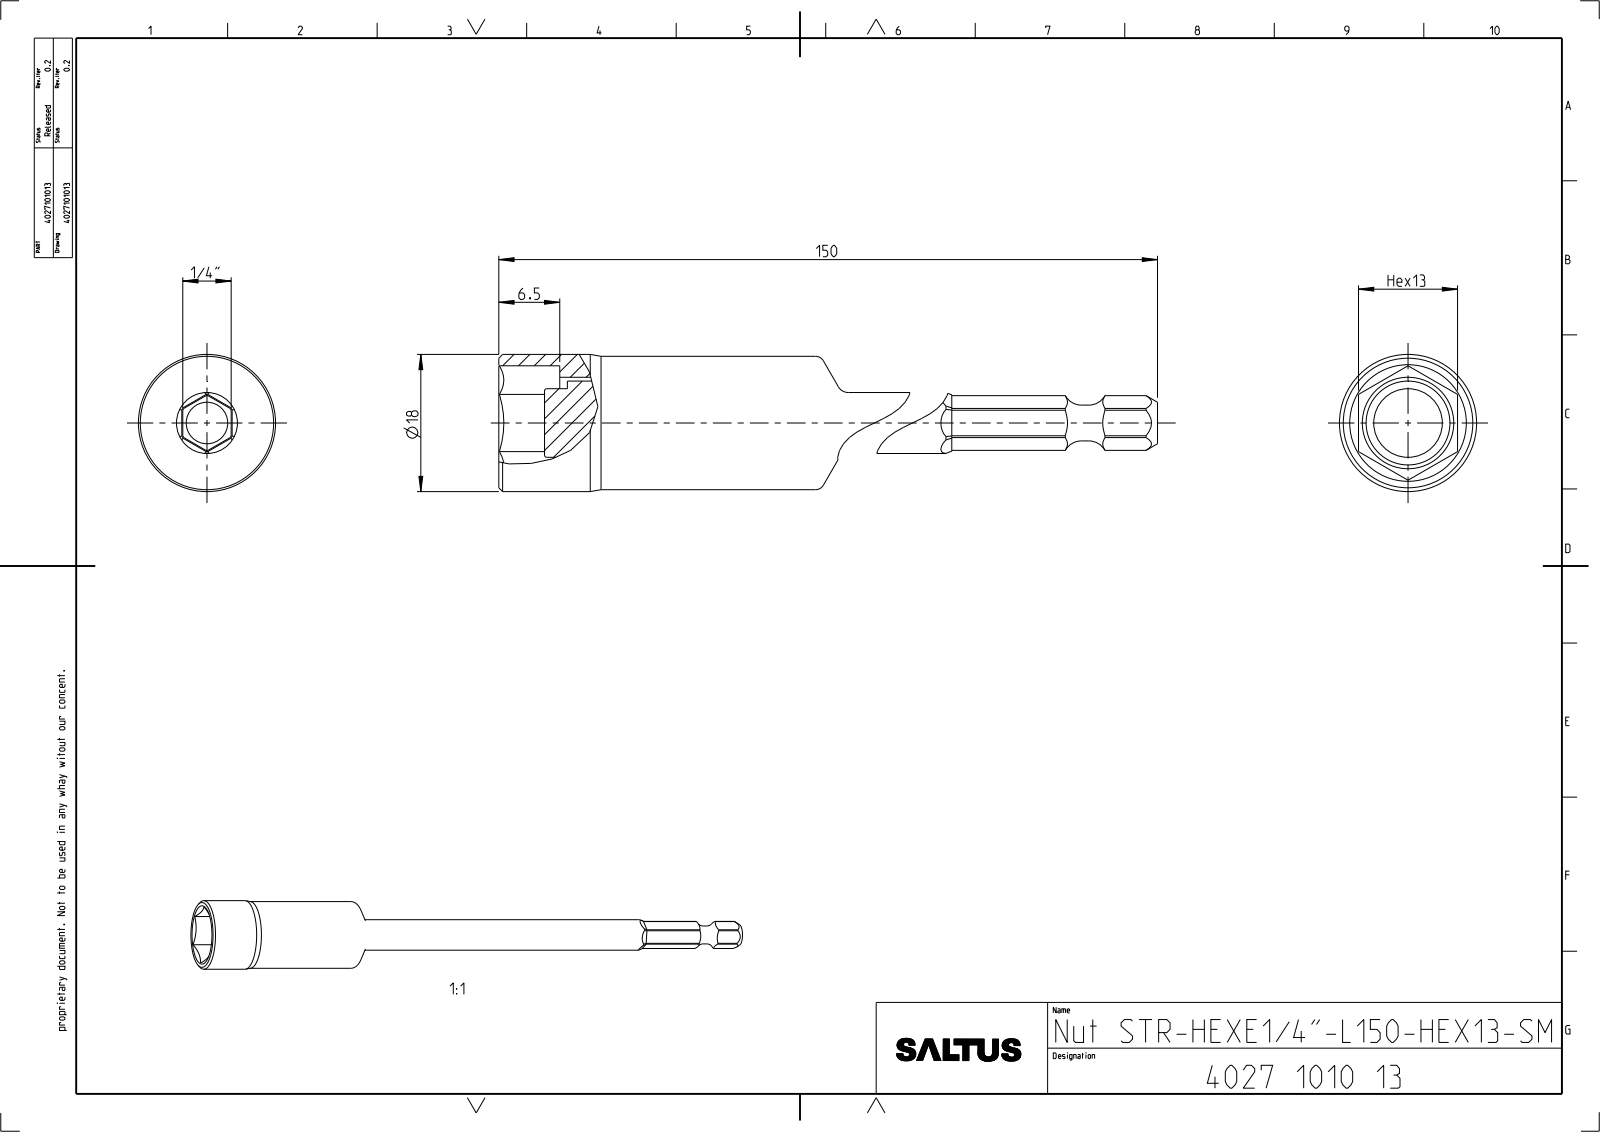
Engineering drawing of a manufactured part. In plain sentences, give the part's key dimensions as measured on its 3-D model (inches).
The part is named "4027101013". Its 3-D file was written by "CREO PARAMETRIC BY PTC INC, 2022414 (CONFIG_CONTROL_DESIGN)". It is 2 solids with 85 faces: 25 planar, 32 cylindrical and 28 other. Overall it measures 5.906 by 0.709 by 0.709 inches. Its volume is 0.826 cubic inches and its surface area 10.52 square inches. Round holes: 1 of diameter 0.472. Round bosses or shafts: 1 of diameter 0.709, 1 of diameter 0.689, 1 of diameter 0.433, 1 of diameter 0.354, 1 of diameter 0.315, 1 of diameter 0.185. Partial cylindrical surfaces (rounded edges, fillets, slot ends): 6 of radius 0.157, 1 of radius 0.141. The main face-to-face distances are 0.131, 0.381, 0.25, 0.512, 0.315, 0.354, 0.433, 0.669, 0.236, 0.079.
